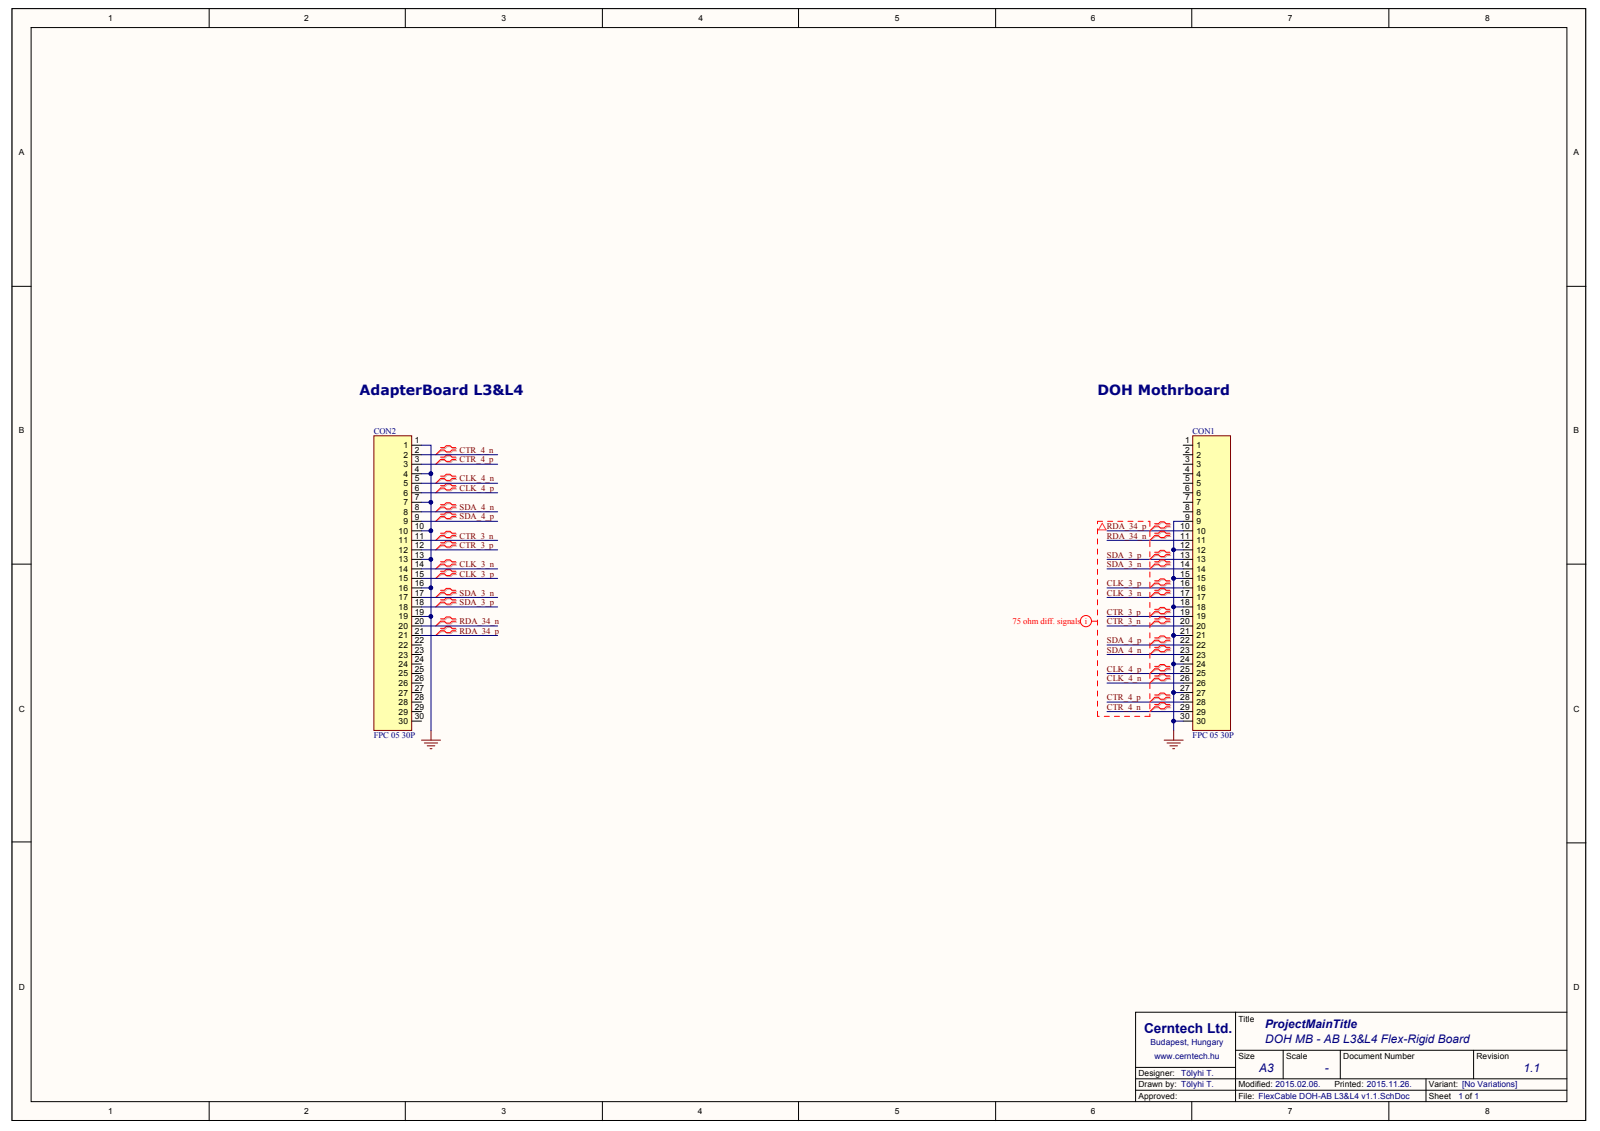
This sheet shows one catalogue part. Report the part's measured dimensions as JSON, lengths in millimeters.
{"part_name": "PCB; BoardFC_DOH_L3&L4_v1.1.3", "step_written_by": "Open CASCADE 6.5 (AUTOMOTIVE_DESIGN)", "units": "millimeters", "bodies": {"solids": 1, "faces": 84, "planar": 84, "cylindrical": 0, "other": 0}, "overall_size": [76.01, 16.61, 0.3], "volume_mm3": 354, "surface_area_mm2": 2415, "face_to_face_distances": [15.5, 76, 0.55, 16.05, 14.99, 15.12, 72.65, 72.66, 17.19, 16.6]}
